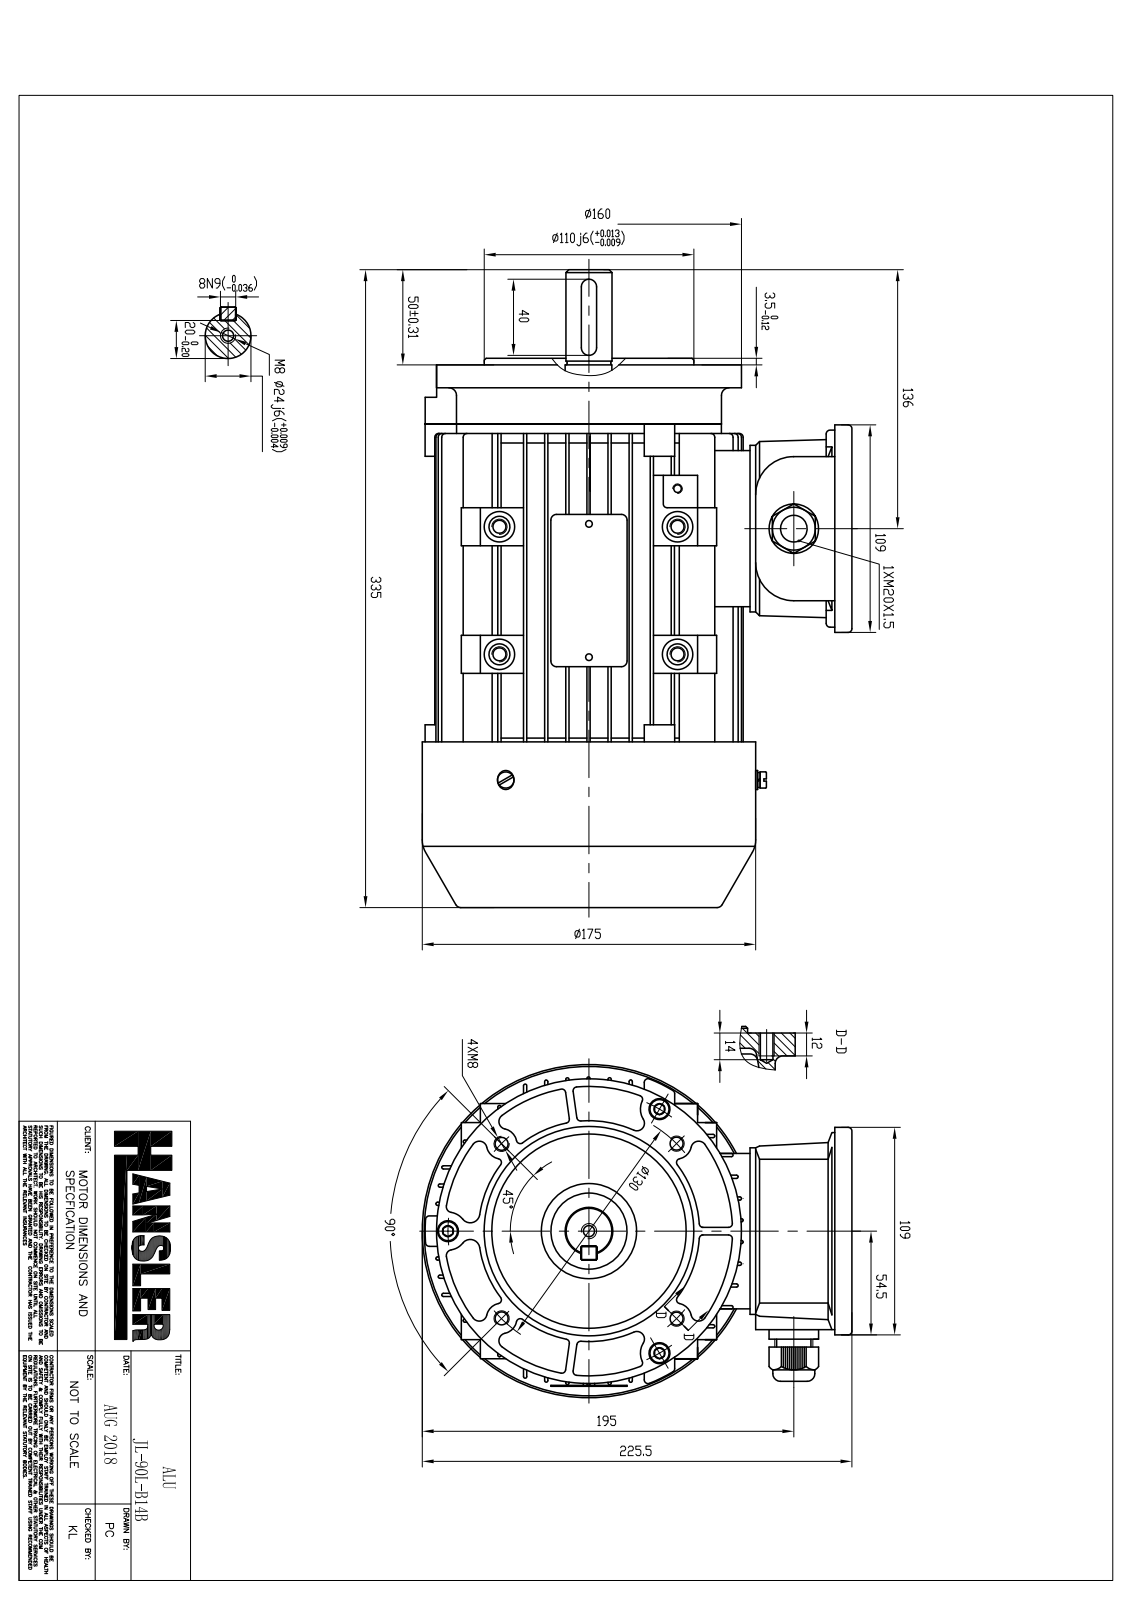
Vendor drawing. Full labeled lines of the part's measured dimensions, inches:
Part name (STEP PRODUCT): JL-90L-B14B
STEP written by: SIEMENS PLM Software NX 12.0 (AP203_CONFIGURATION_CONTROLLED_3D_DESIGN_OF_MECHANICAL_PARTS_AND_ASSEMBLIES_MIM_LF)
Units: inches
Bodies: 41 solids, 3986 faces (2442 planar, 1181 cylindrical, 363 other)
Overall size (bounding box): 13.189 × 8.976 × 6.89
Volume: 81.59 in³ · Surface area: 1 313 in²
Round holes (diameter × count): ⌀0.315 ×14, ⌀0.157 ×13, ⌀0.197 ×11, ⌀0.228 ×10, ⌀0.63 ×8, ⌀0.189 ×4, ⌀0.207 ×4, ⌀0.209 ×4, ⌀0.236 ×3, ⌀0.252 ×3, ⌀0.276 ×3, ⌀0.433 ×3
Round bosses / shafts (diameter × count): ⌀0.433 ×8, ⌀0.176 ×8, ⌀0.394 ×7, ⌀0.472 ×4, ⌀0.309 ×4, ⌀0.197 ×4, ⌀0.378 ×3, ⌀0.211 ×3
Partial cylindrical surfaces — rounded edges, fillets, slot ends (radius × count): R0.02 ×464, R0.079 ×70, R0.157 ×27, R0.03 ×16, R0.059 ×14, R0.118 ×13, R0.197 ×10, R0.276 ×8
Main face-to-face distances: 0.067, 0.436, 1.745, 0.872, 0.197, 0.098, 2.181, 0.369, 0.079, 0.503
Hole centre spacings: 1.398, 2, 2.248, 2.856, 3.034, 0.866, 0.591, 0.613
